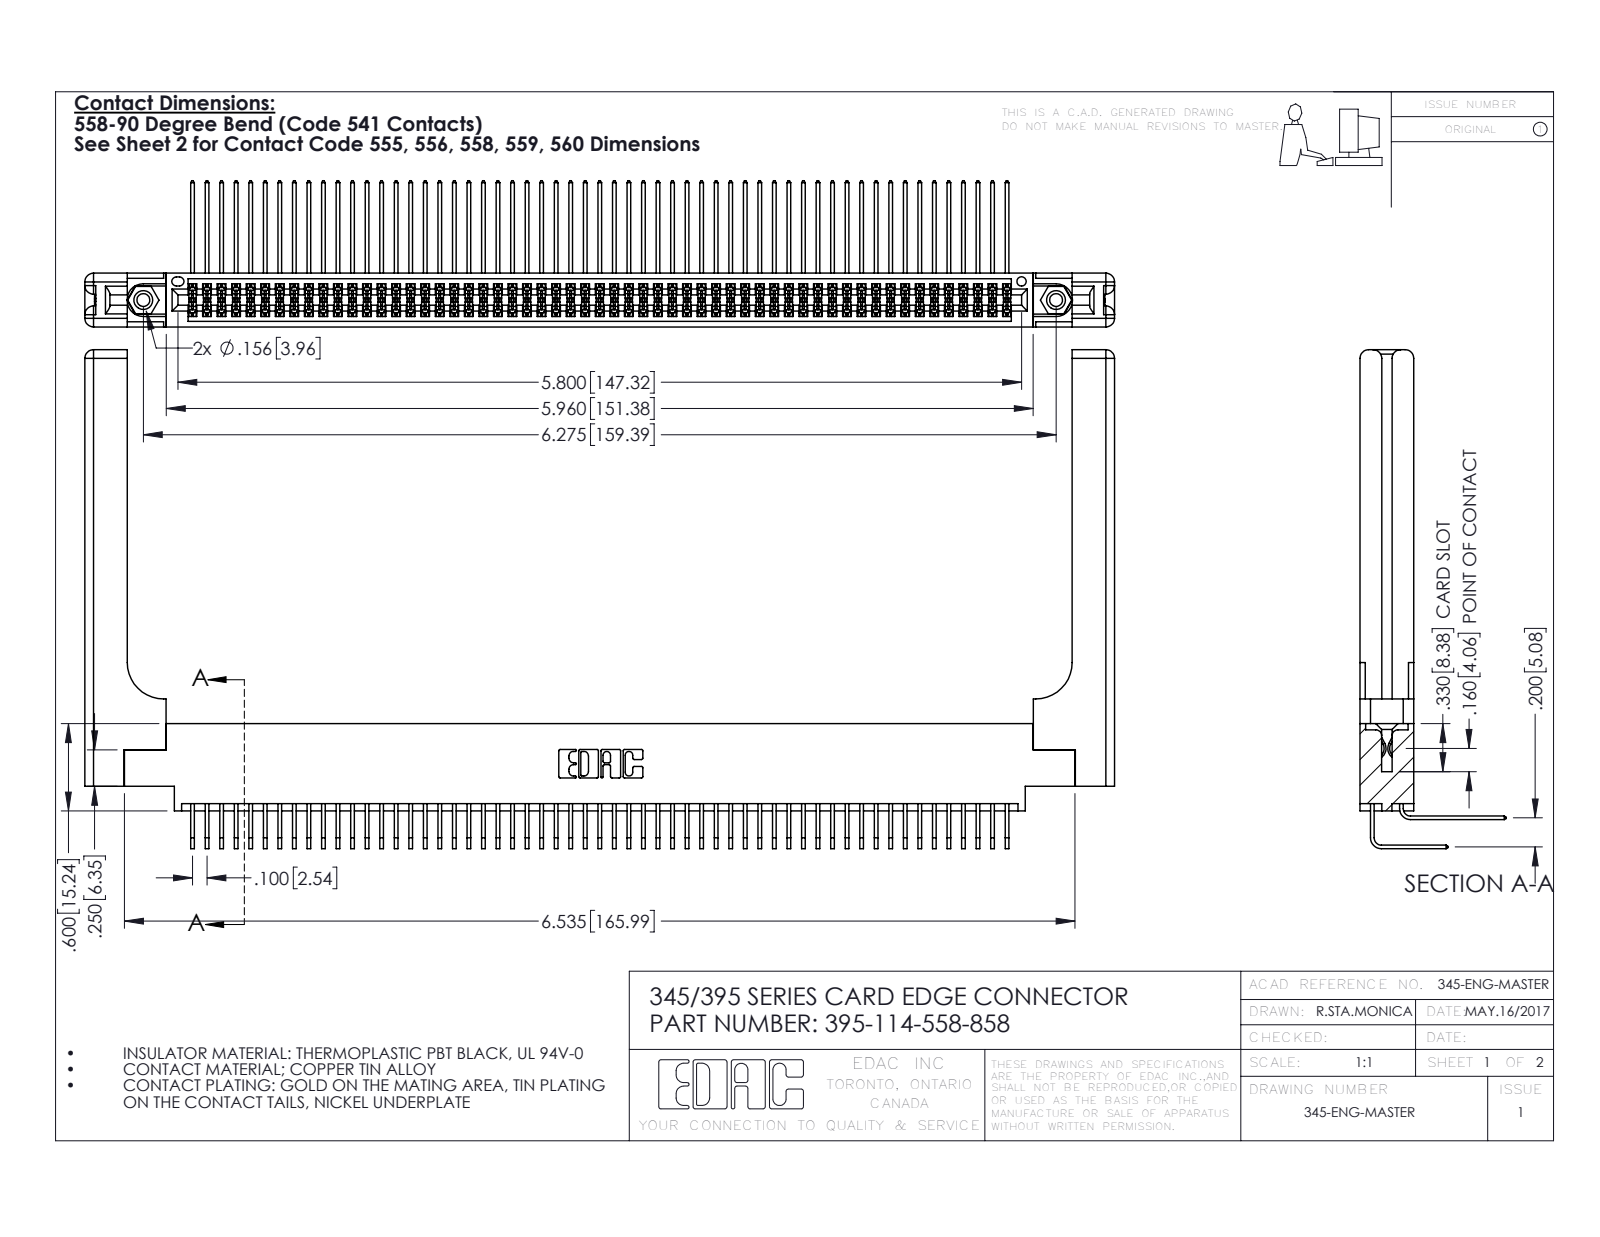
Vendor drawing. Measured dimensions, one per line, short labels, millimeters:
name: 345-292-001_558 Tail - 2; 345-292-001_558 559 Tail - 1; 345-250-001_345-250-001-102; 345 Part_0.170 Offset - 0.156 Dia-TH (+2 more)
written by: SolidWorks 2016 (CONFIG_CONTROL_DESIGN)
unit: mm
bodies: 119 solids, 6314 faces (4222 planar, 2032 cylindrical, 60 other)
size: 179.8 × 87.1 × 25.5
volume: 26 630 mm³; area: 35 410 mm²
holes: 2× ⌀2.3, 2× ⌀3.2, 2× ⌀4, 1× ⌀1.6
bosses: 2× ⌀3.9
rounds: 172× R0.2, 22× R0.3, 16× R1.5, 6× R0.2, 6× R0.8, 3× R0.7, 2× R0.4, 2× R0.5
face distances: 1.8, 7.6, 9.4, 5.1, 2.5, 6.9, 0.6, 5.7, 4.4, 3.8
hole spacings: 6.9, 153.4, 159.4
